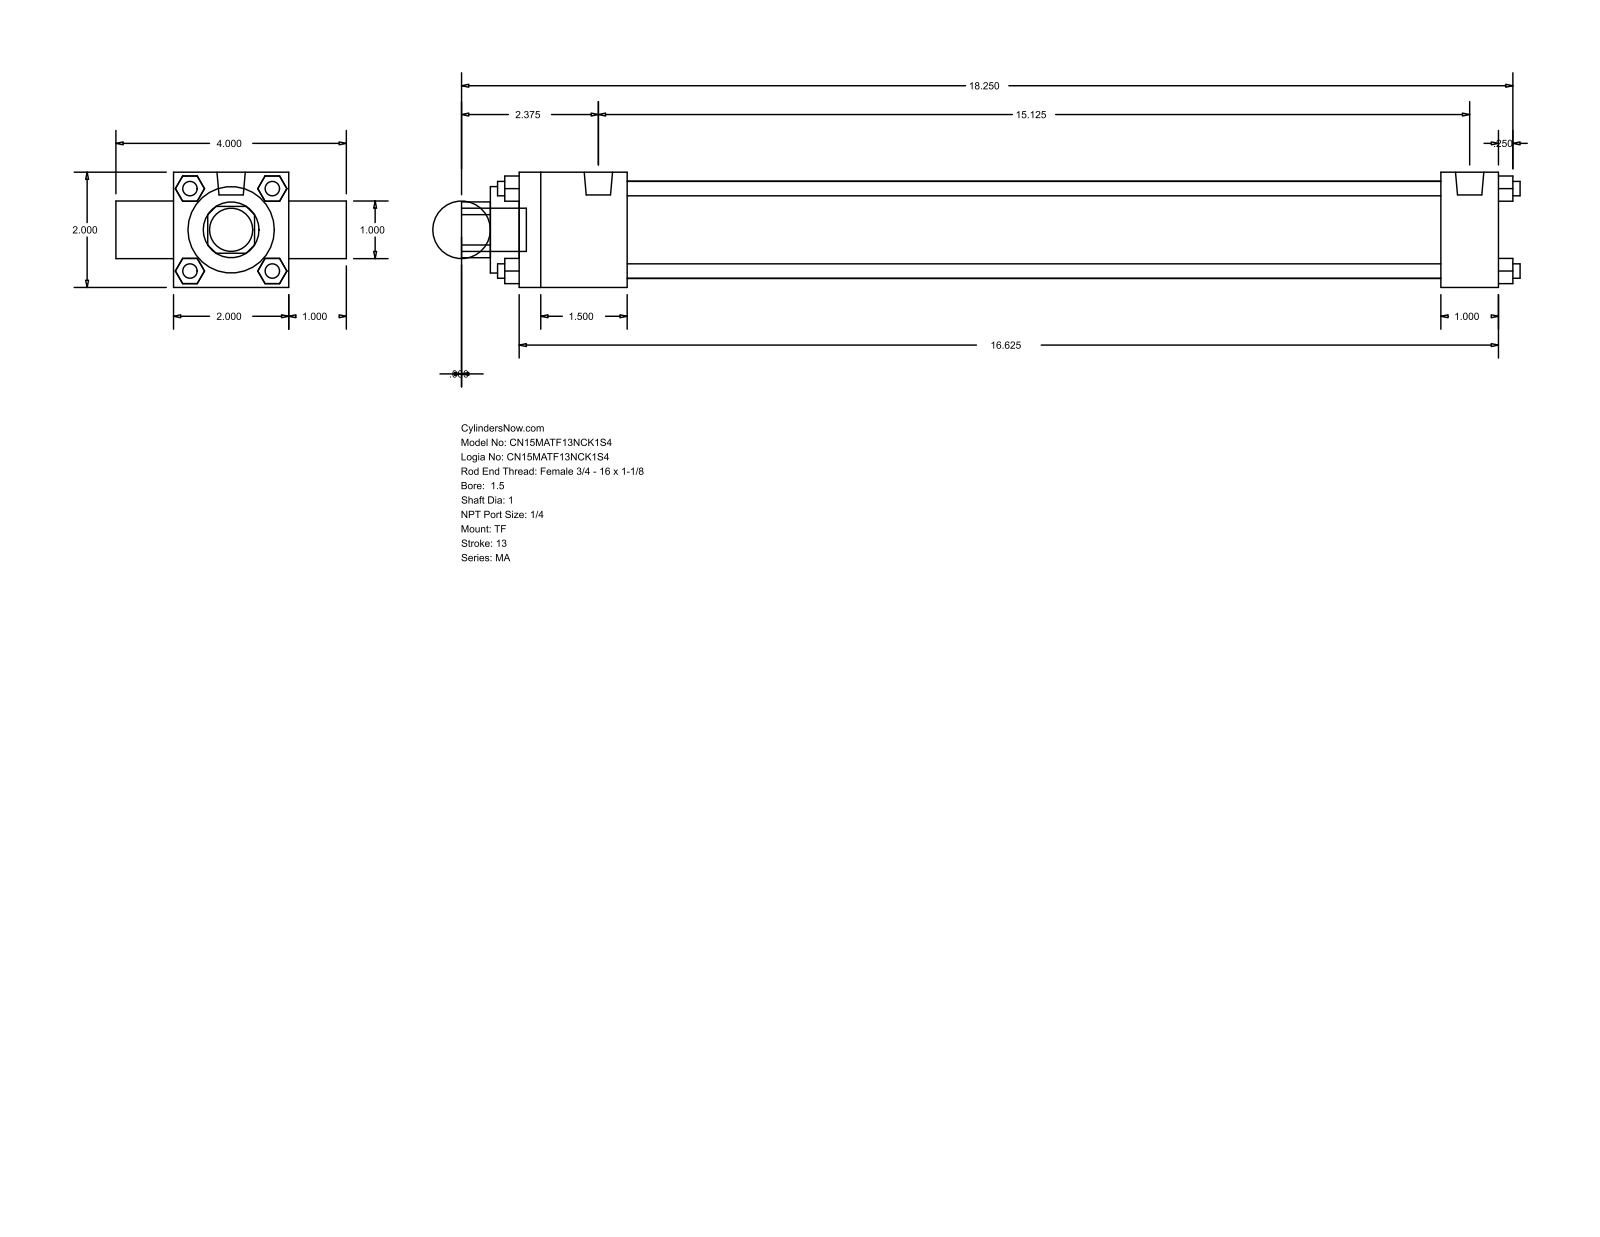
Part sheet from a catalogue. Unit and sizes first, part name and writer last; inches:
Units: inches
Overall size (bounding box): 18.375 × 4 × 2
Round holes (diameter × count): ⌀1 ×2, ⌀1.5 ×1, ⌀1.69 ×1
Round bosses / shafts (diameter × count): ⌀0.25 ×4, ⌀0.313 ×3, ⌀0.492 ×2, ⌀0.75 ×1
Partial cylindrical surfaces — rounded edges, fillets, slot ends (radius × count): R0.484 ×1
Main face-to-face distances: 2, 1, 17, 3, 0.25, 1.875, 16, 14.125, 15.125, 17.5
Bodies: 0 solids, 120 faces (92 planar, 28 cylindrical, 0 other)
Part name (STEP PRODUCT): MA_TF__0150_1
STEP written by: GSSL Pune (CONFIG_CONTROL_DESIGN)
